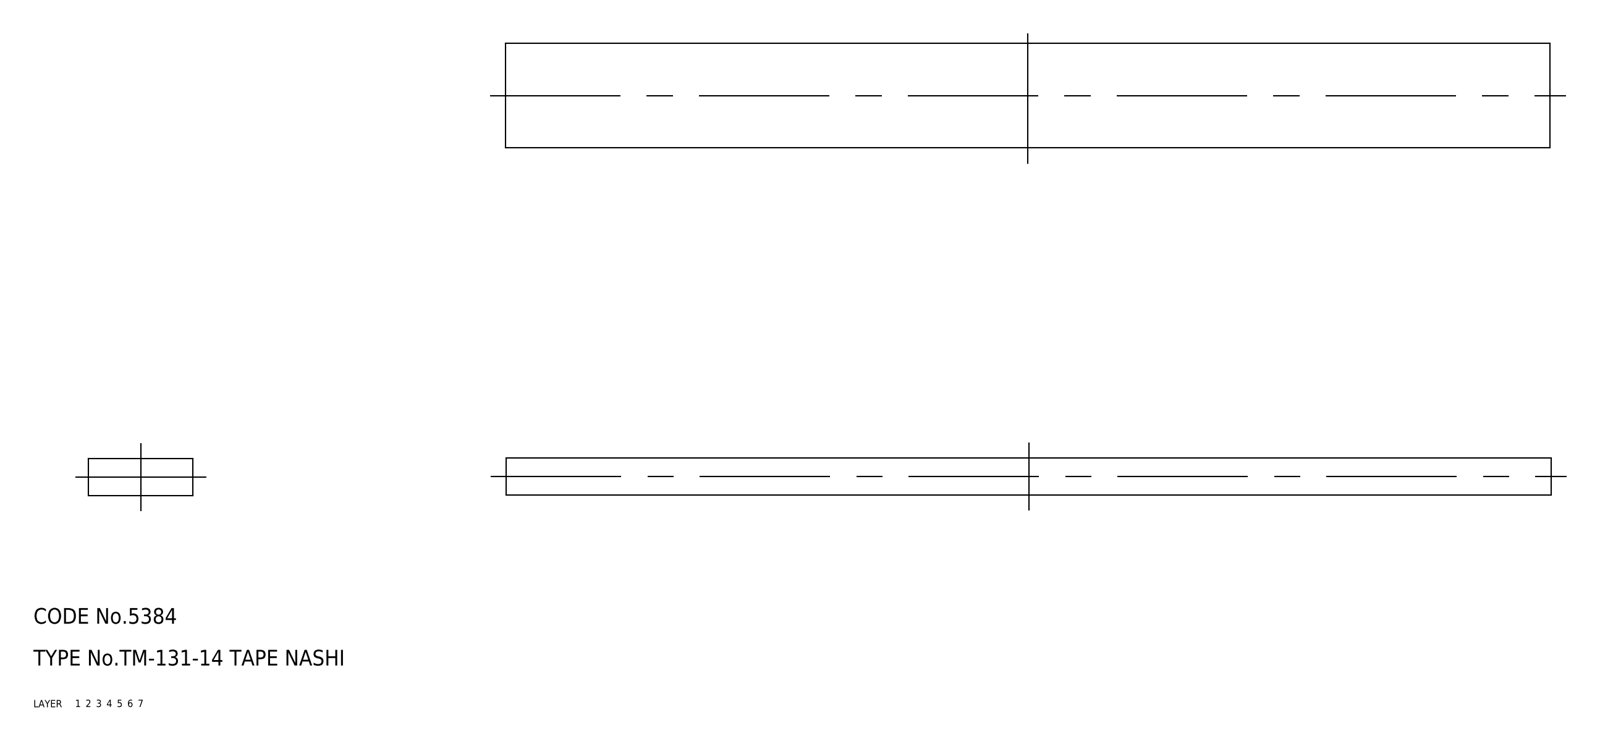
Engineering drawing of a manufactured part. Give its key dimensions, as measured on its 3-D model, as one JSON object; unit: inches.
{"part_name": "rubber foam", "step_written_by": "CADfix (AUTOMOTIVE_DESIGN)", "units": "inches", "bodies": {"solids": 1, "faces": 6, "planar": 0, "cylindrical": 0, "other": 6}, "overall_size": [7.874, 0.787, 0.276], "volume_in3": 1.709, "surface_area_in2": 17.17}
